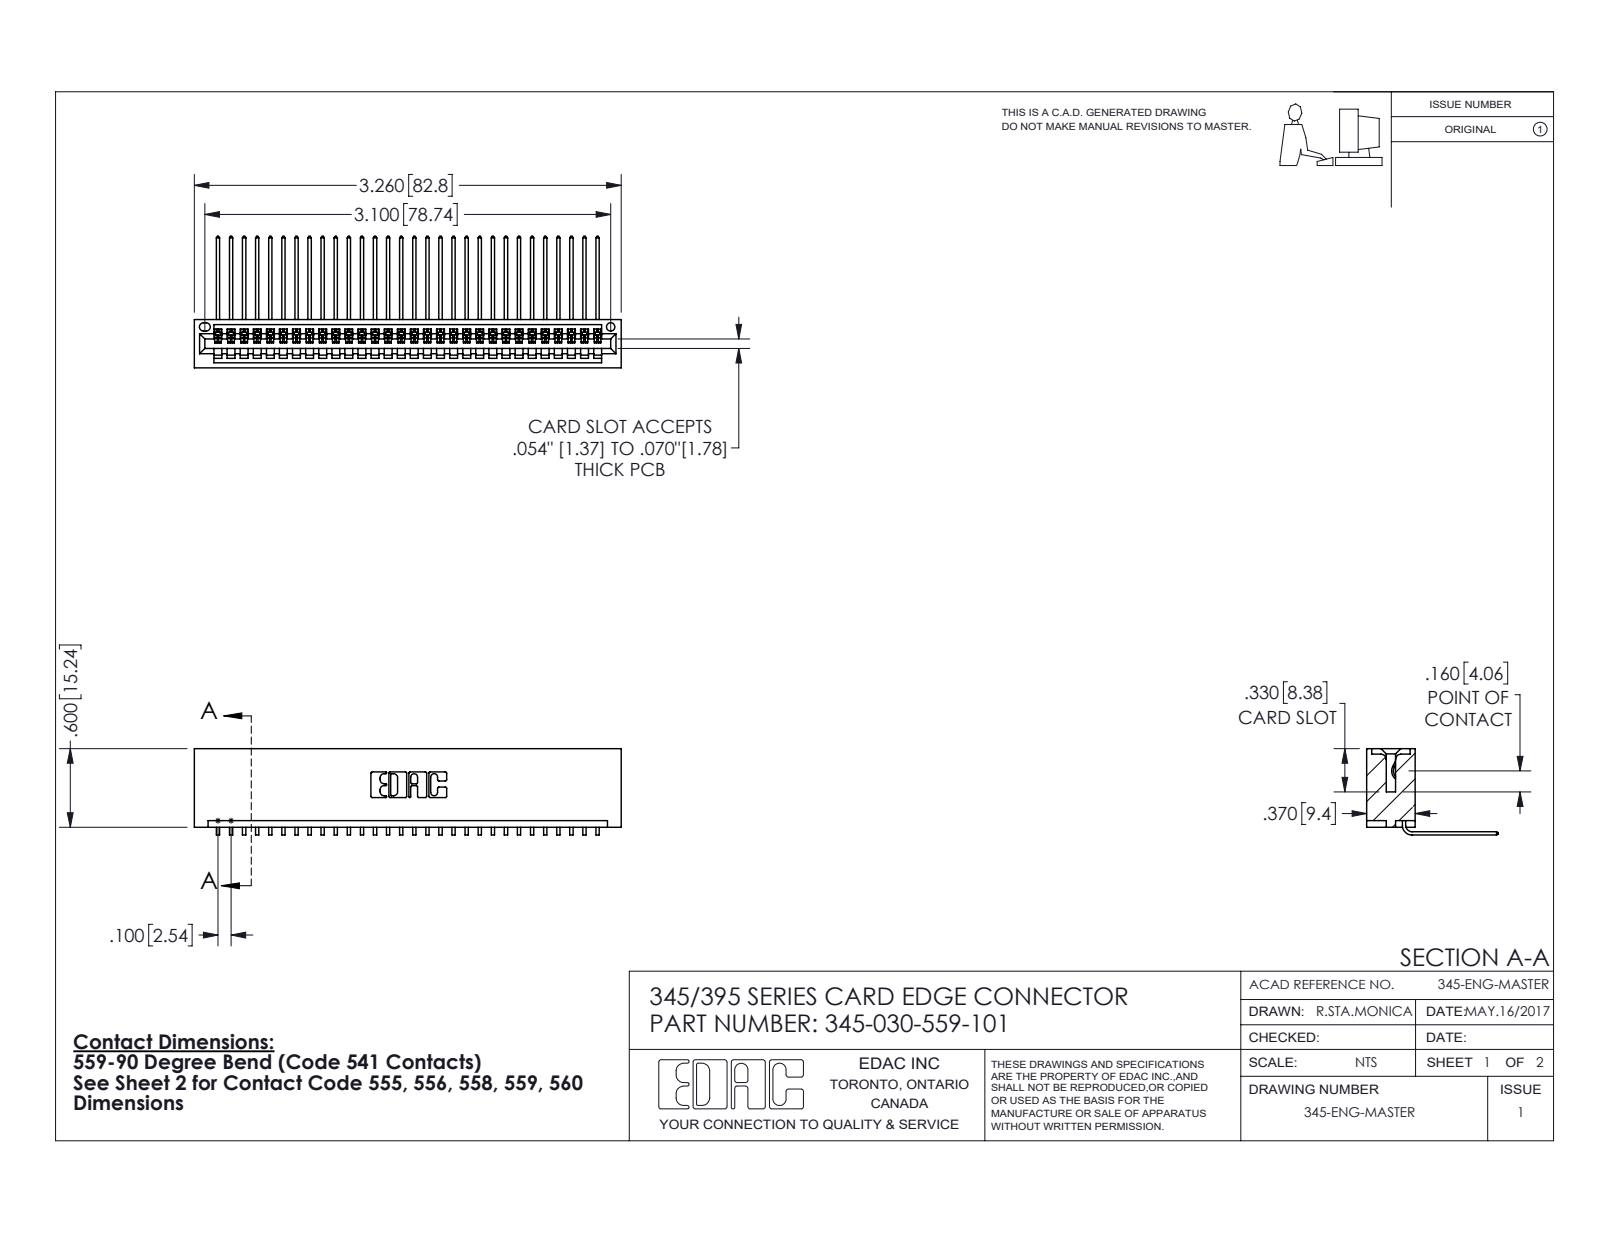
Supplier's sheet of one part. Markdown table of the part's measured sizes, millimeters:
| quantity | value |
| --- | --- |
| part name | 345-292-001_558 559 Tail - 1; 345 Part_No Mounting Lugs; 345-030-559-101 |
| STEP written by | SolidWorks 2016 (CONFIG_CONTROL_DESIGN) |
| units | millimeters |
| bodies | 31 solids, 1918 faces (1336 planar, 582 cylindrical, 0 other) |
| overall size | 82.8 × 25.5 × 16.7 |
| volume | 8 460 mm³ |
| surface area | 11 850 mm² |
| round holes (diameter × count) | 1.6 × 1 |
| partial cylindrical surfaces (radius × count) | 0.2 × 60, 0.3 × 22, 0.2 × 6, 0.8 × 6, 0.7 × 3, 0.8 × 2, 1 × 2, 0.4 × 1 |
| main face-to-face distances | 7.6, 1.8, 9.4, 5.1, 2.5, 6.9, 0.6, 5.7, 3.8, 1.8 |
